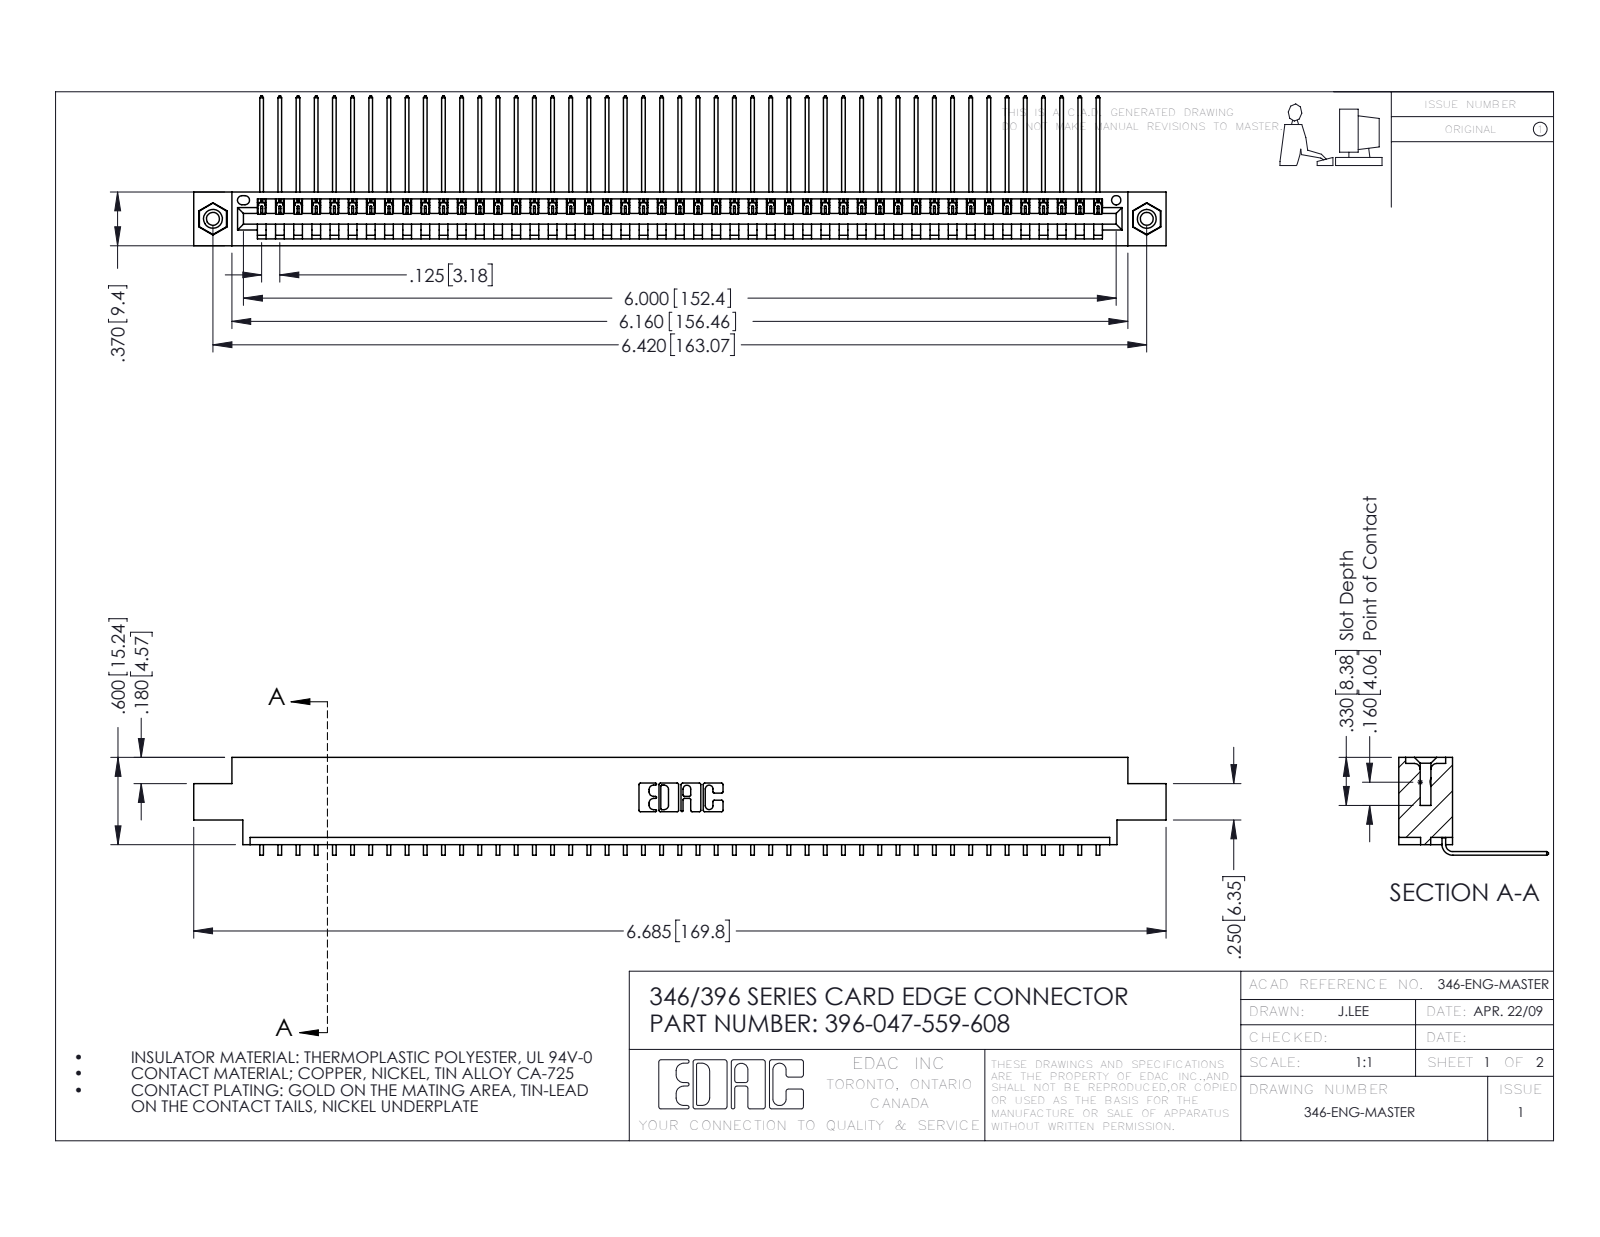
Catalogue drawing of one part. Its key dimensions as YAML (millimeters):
part_name: "346 Part_0.170 Offset - 0.156 Dia-TI; 396-047-559-608; 345-250-001_345-250-003-102; 345-292-001_558 559 Tail - 1"
step_written_by: "SolidWorks 2016 (CONFIG_CONTROL_DESIGN)"
units: millimeters
bodies: {solids: 50, faces: 3006, planar: 2086, cylindrical: 904, other: 16}
overall_size: [169.8, 26.2, 17.1]
volume: 16300
surface_area: 21520
round_holes:
  - {diameter: 2.3, count: 2}
  - {diameter: 3.2, count: 2}
  - {diameter: 4, count: 2}
  - {diameter: 1.6, count: 1}
round_bosses_or_shafts:
  - {diameter: 3.9, count: 2}
partial_cylinders:
  - {radius: 0.2, count: 94}
  - {radius: 0.3, count: 22}
  - {radius: 0.2, count: 6}
  - {radius: 0.8, count: 6}
  - {radius: 0.7, count: 3}
  - {radius: 0.8, count: 2}
  - {radius: 1, count: 2}
  - {radius: 0.4, count: 1}
face_to_face_distances: [1.2, 8.2, 9.4, 0.6, 6.4, 1.8, 5.6, 7.6, 3.8, 2.5]
hole_center_spacings: [6.2, 157.8, 163.1]
